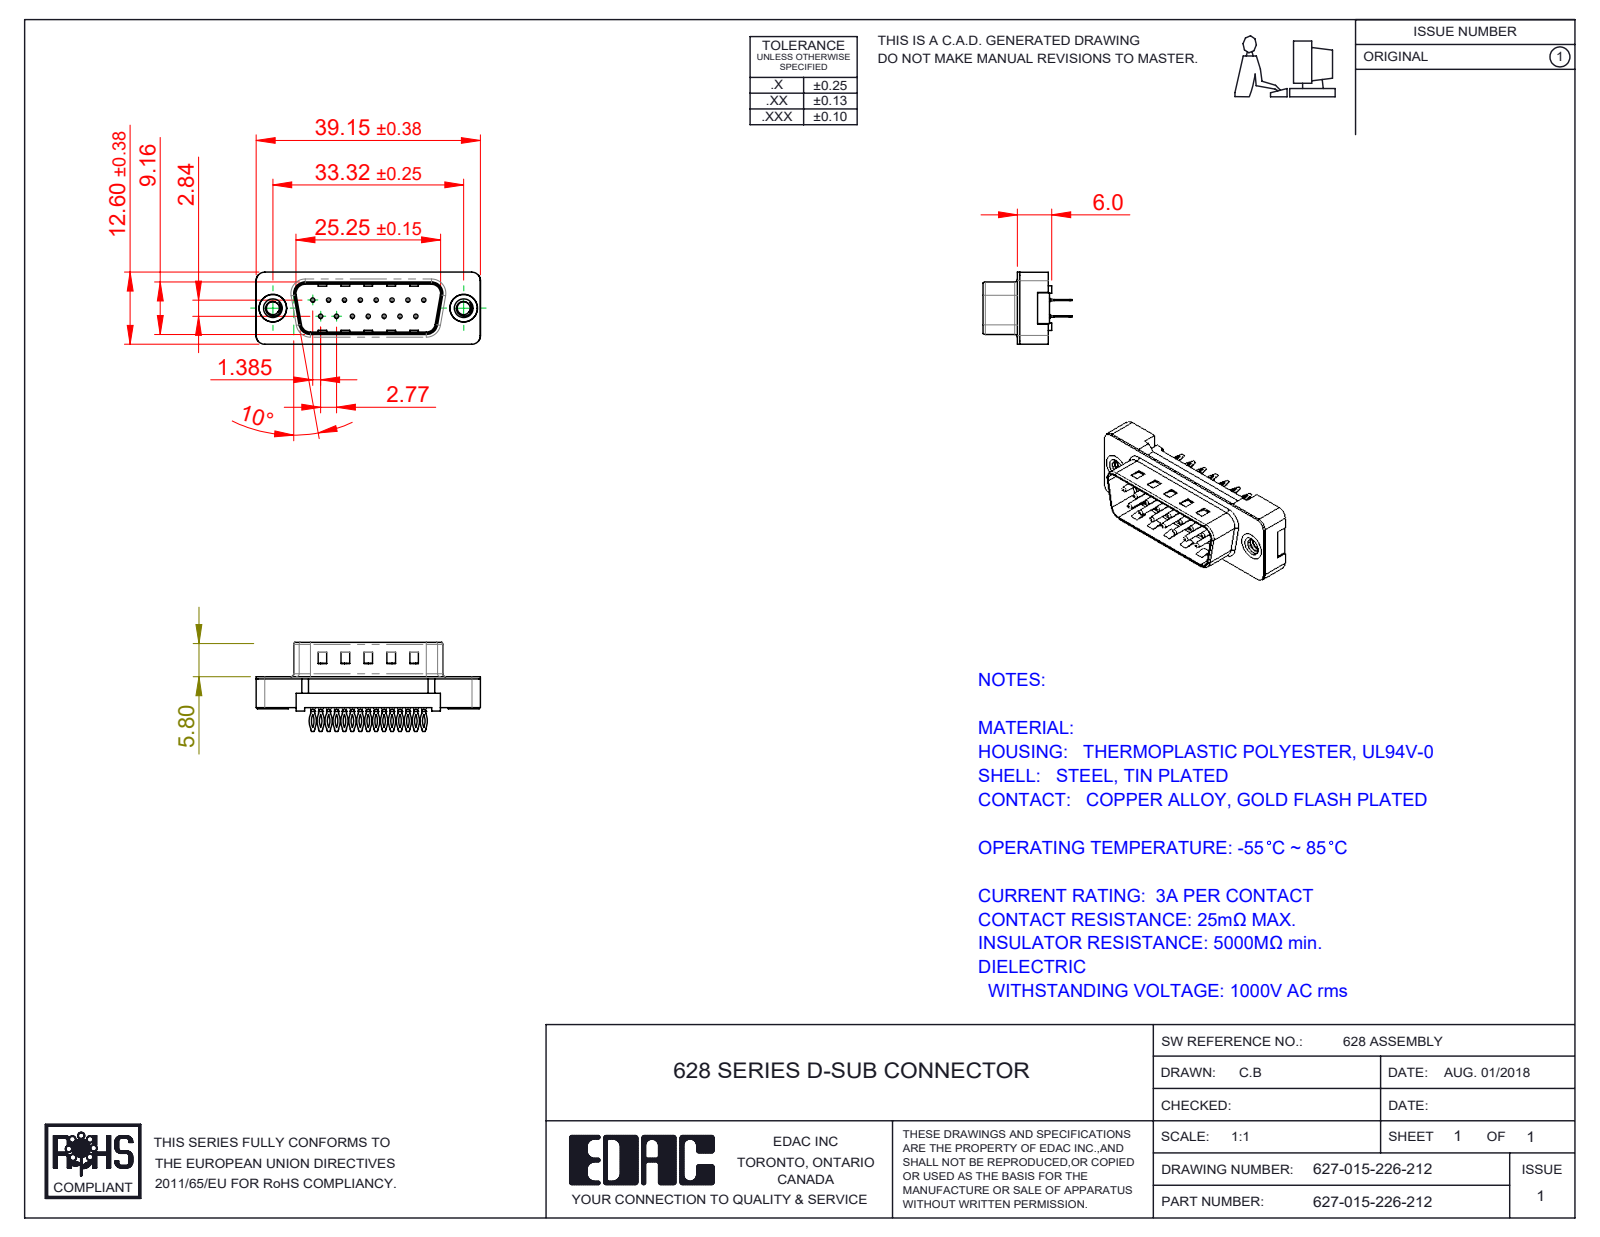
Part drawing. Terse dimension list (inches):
name: 627 PB Contact Row 1_26; 627 PB Contact Row 2_26; 627 PB 4-40 Threaded Rivet; 627 Plastic Body Housing_15 Contacts (+2 more)
written by: SolidWorks 2020 (CONFIG_CONTROL_DESIGN)
unit: in
bodies: 19 solids, 1356 faces (816 planar, 400 cylindrical, 140 other)
size: 1.543 × 0.612 × 0.496
volume: 0.121 in³; area: 6.62 in²
holes: 15× ⌀0.014, 15× ⌀0.033, 2× ⌀0.089, 2× ⌀0.157, 2× ⌀0.189, 2× ⌀0.197
bosses: 15× ⌀0.03, 2× ⌀0.193
rounds: 30× R0.01, 30× R0.115, 30× R0.131, 15× R0.005, 8× R0.02, 8× R0.059, 4× R0.035, 4× R0.063
face distances: 0.016, 0.098, 0.213, 0.345, 0.197, 0.114, 0.334, 0.027, 0.318, 0.094
hole spacings: 0.124, 0.109, 0.218, 0.327, 0.198, 0.294, 0.436, 0.198
